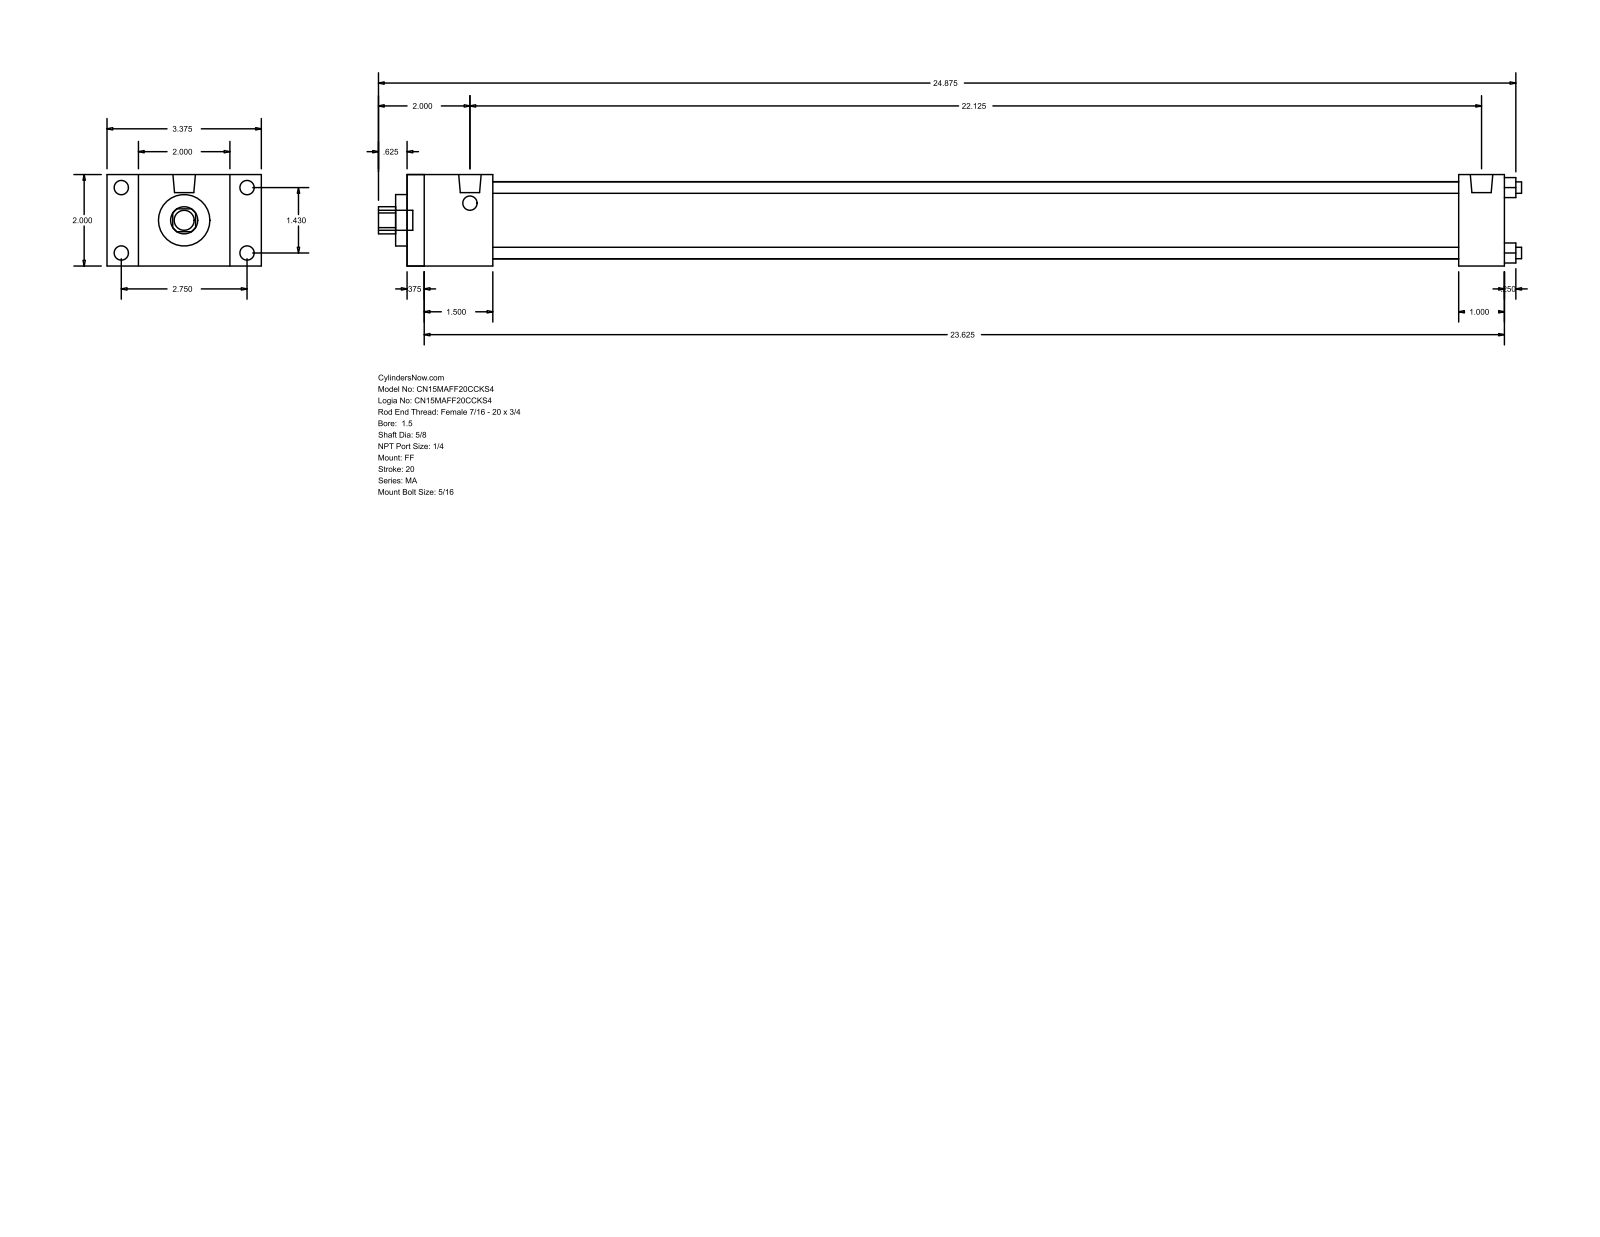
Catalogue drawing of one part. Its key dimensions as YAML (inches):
part_name: "MA_FF__0150_0.625"
step_written_by: "GSSL Pune (CONFIG_CONTROL_DESIGN)"
units: inches
bodies: {solids: 0, faces: 92, planar: 64, cylindrical: 28, other: 0}
overall_size: [25, 3.375, 2]
round_holes:
  - {diameter: 0.25, count: 4}
  - {diameter: 0.625, count: 1}
  - {diameter: 1.125, count: 1}
  - {diameter: 1.69, count: 1}
round_bosses_or_shafts:
  - {diameter: 0.313, count: 8}
  - {diameter: 0.492, count: 2}
  - {diameter: 0.437, count: 1}
partial_cylinders:
  - {radius: 0.297, count: 1}
face_to_face_distances: [2, 24, 0.375, 23.625, 1, 1.875, 23, 1.5, 22.625, 21.125]
hole_center_spacings: [1.011, 1.43, 2.022]
